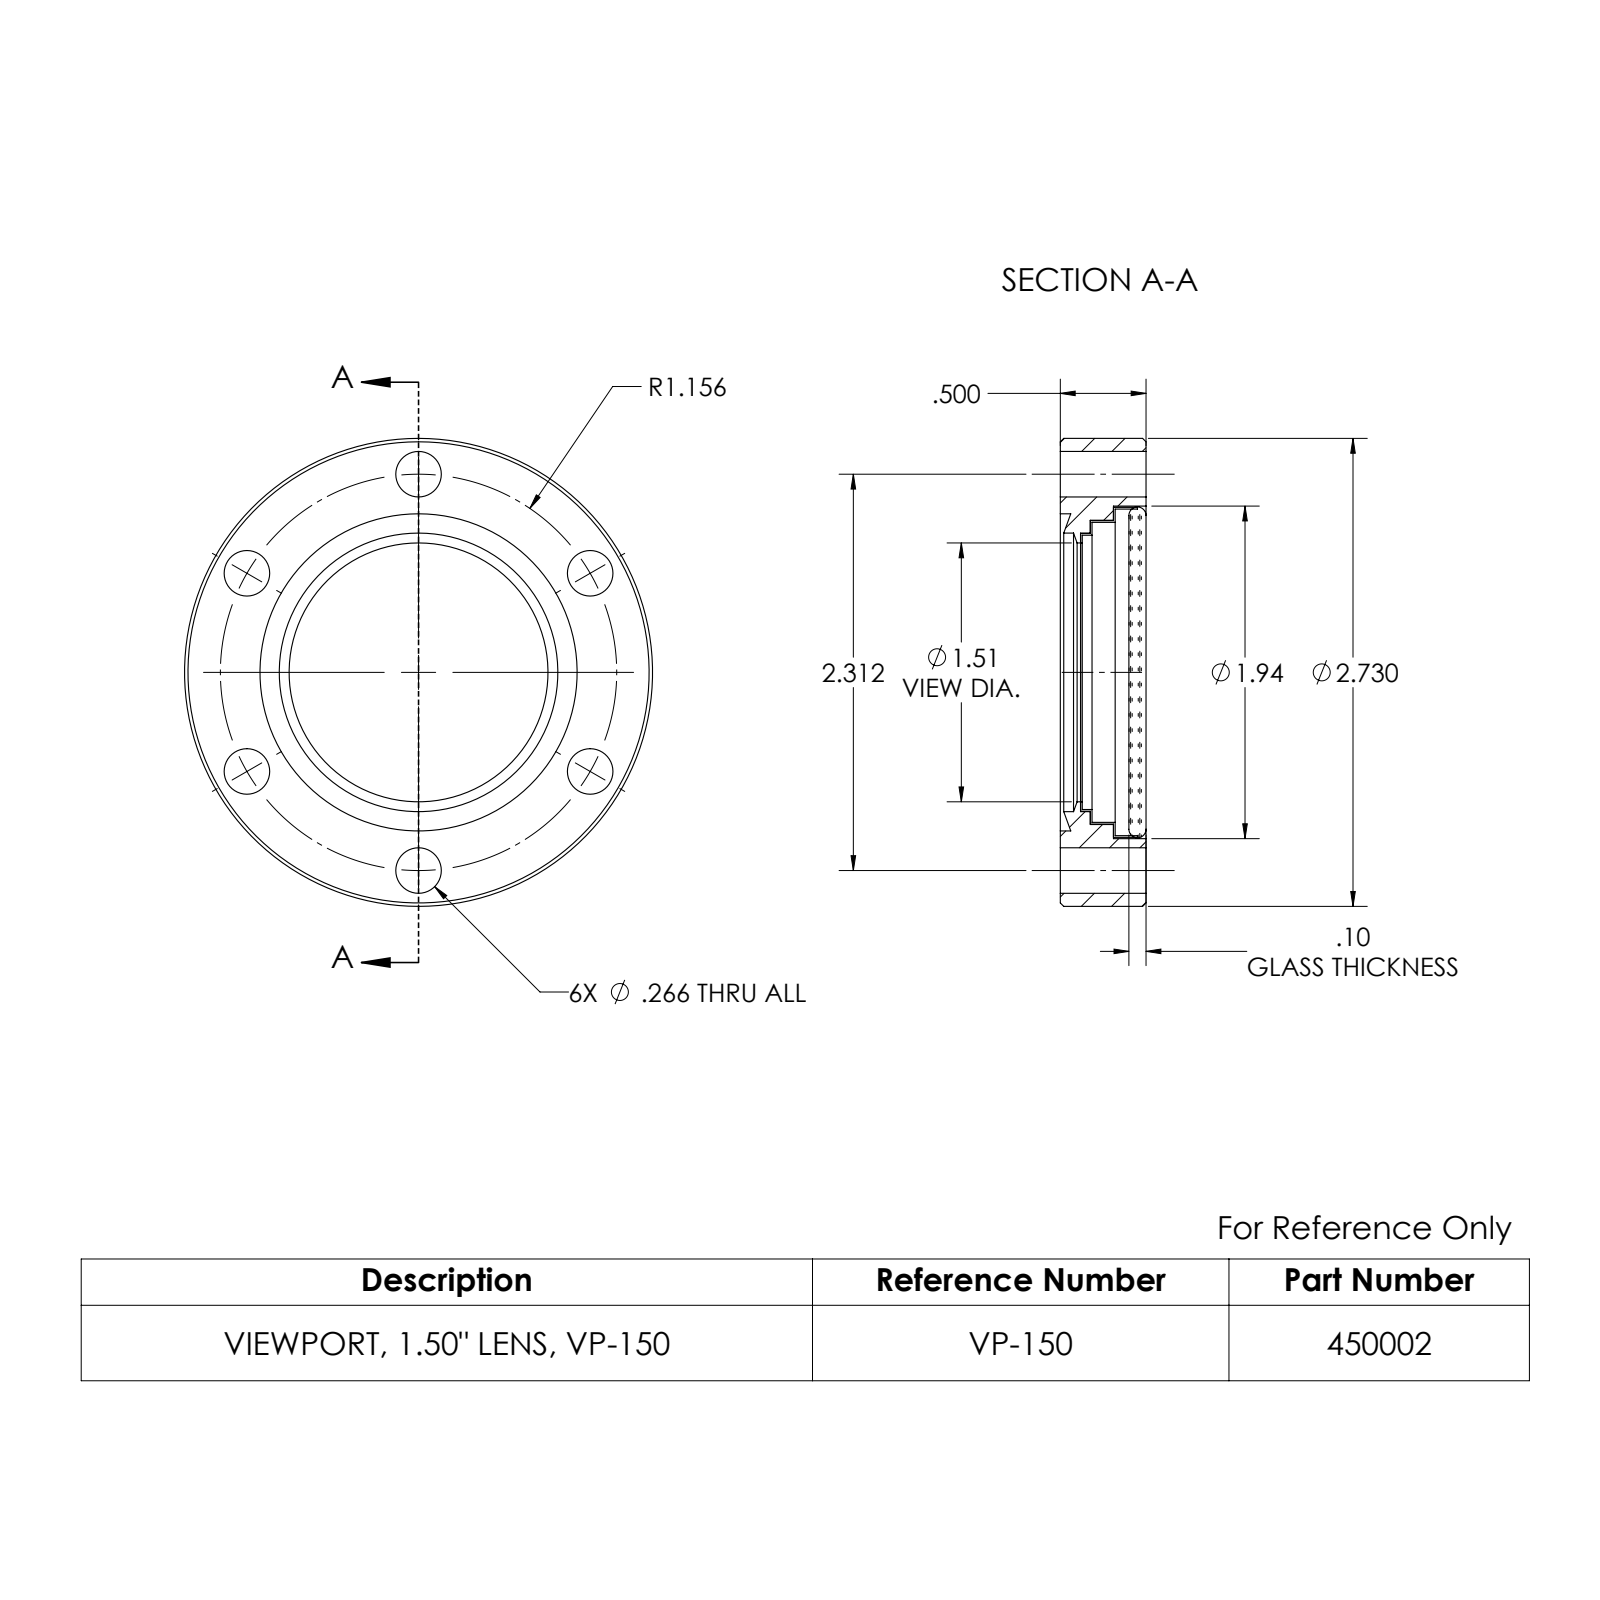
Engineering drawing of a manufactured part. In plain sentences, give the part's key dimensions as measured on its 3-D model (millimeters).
The part is named "450002". Its 3-D file was written by "SolidWorks 2022 (AUTOMOTIVE_DESIGN)". It is 2 solids with 41 faces: 7 planar, 26 cylindrical and 8 other. Overall it measures 69.3 by 69.3 by 12.7 millimeters. Its volume is 29 090 cubic millimeters and its surface area 15 170 square millimeters. Round holes: 6 of diameter 6.8, 1 of diameter 38.4, 1 of diameter 41.3, 1 of diameter 45.1, 1 of diameter 47, 1 of diameter 49.3. Round bosses or shafts: 1 of diameter 69.3. The main face-to-face distances are 12.7, 10.2, 2.5, 7.9, 2.3, 4.8, 4.4, 3.4, 5.7, 8.3. The hole center spacings are 29.4, 50.9, 50.9, 58.7, 58.7.
